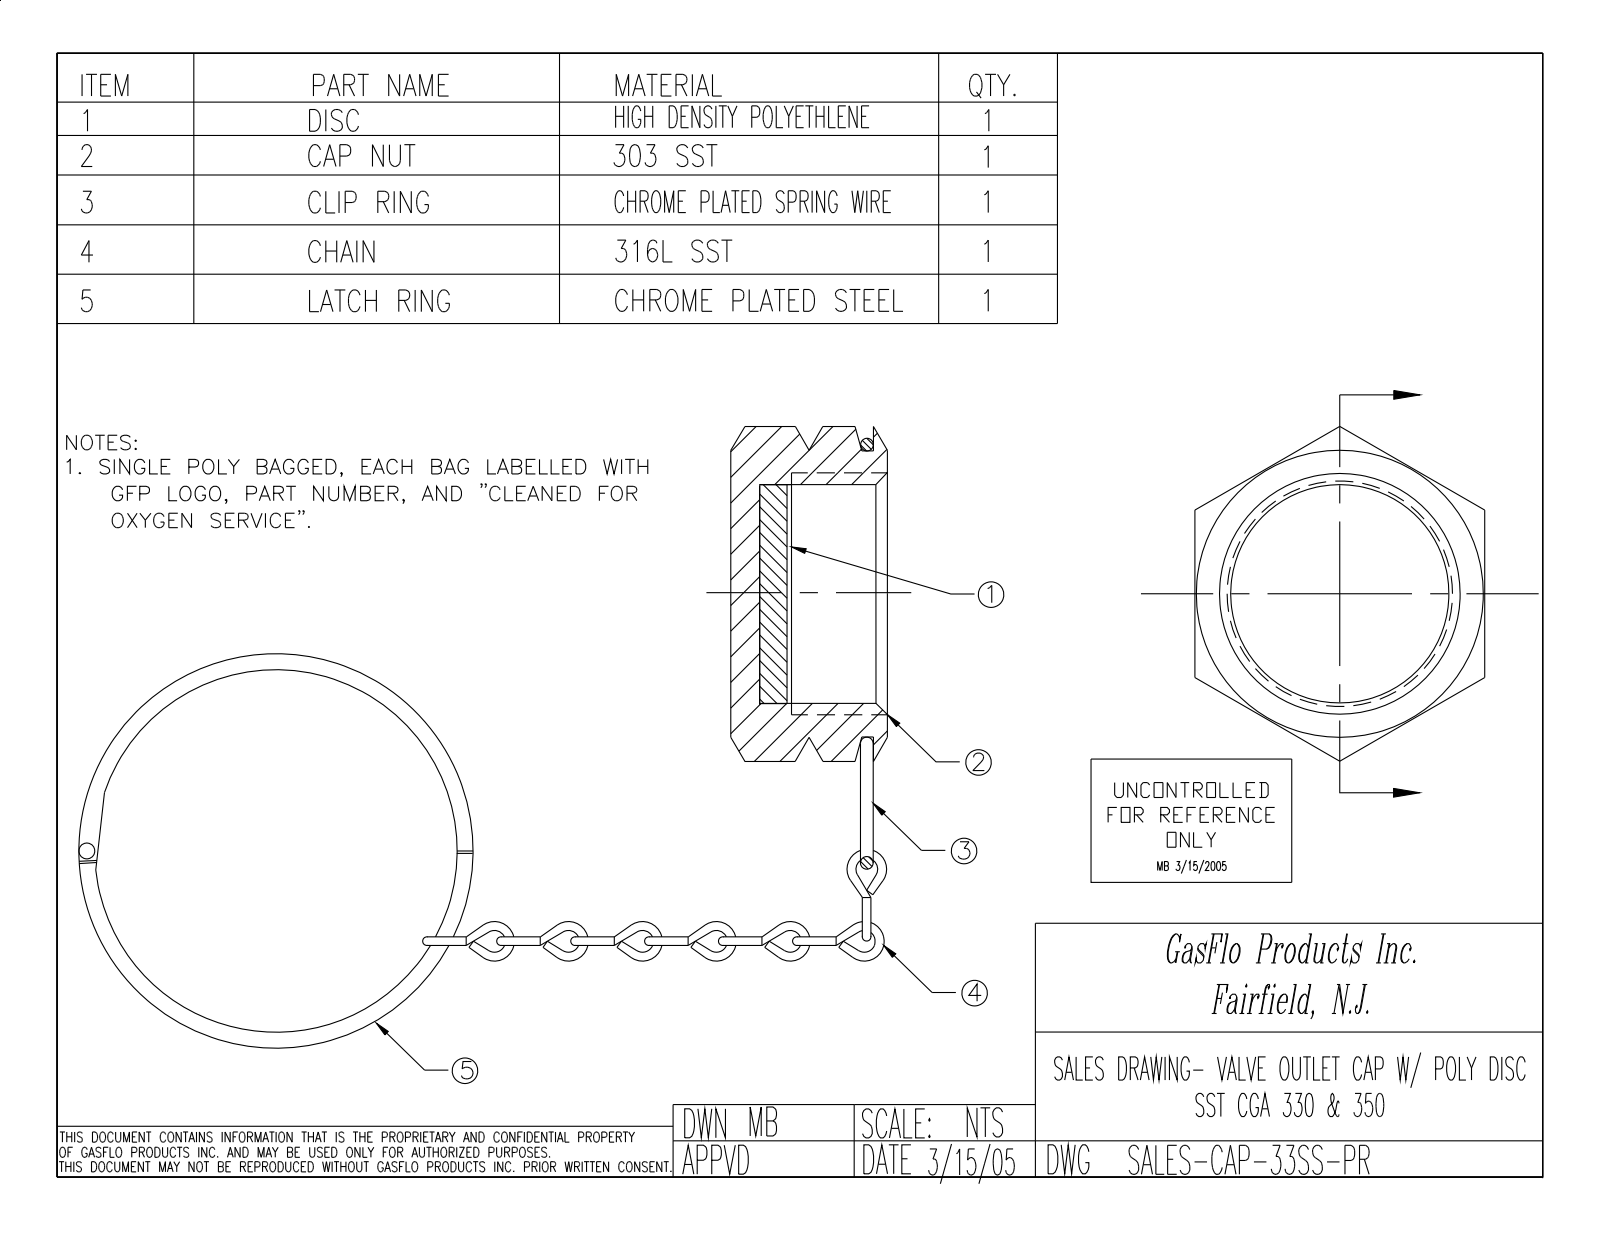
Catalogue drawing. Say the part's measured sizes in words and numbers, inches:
The part is named "PRT-002239_STAINLESS; PRT-000160; ASY-000291; ASY-000211_One Link Bent (+5 more)". Its 3-D file was written by "SolidWorks 2018 (CONFIG_CONTROL_DESIGN)". It is 14 solids with 322 faces: 57 planar, 119 cylindrical and 146 other. Overall it measures 4.206 by 1.789 by 1.233 inches. Its volume is 0.372 cubic inches and its surface area 11.07 square inches. Round holes: 1 of diameter 0.063, 1 of diameter 0.757. Round bosses or shafts: 30 of diameter 0.063, 1 of diameter 0.993, 1 of diameter 0.757, 1 of diameter 0.1. Partial cylindrical surfaces (rounded edges, fillets, slot ends): 24 of radius 0.005, 4 of radius 0.25, 2 of radius 0.01. The main face-to-face distances are 1, 0.1, 0.194, 0.094, 0.1, 0.094, 1, 0.54, 0.44, 0.44.
